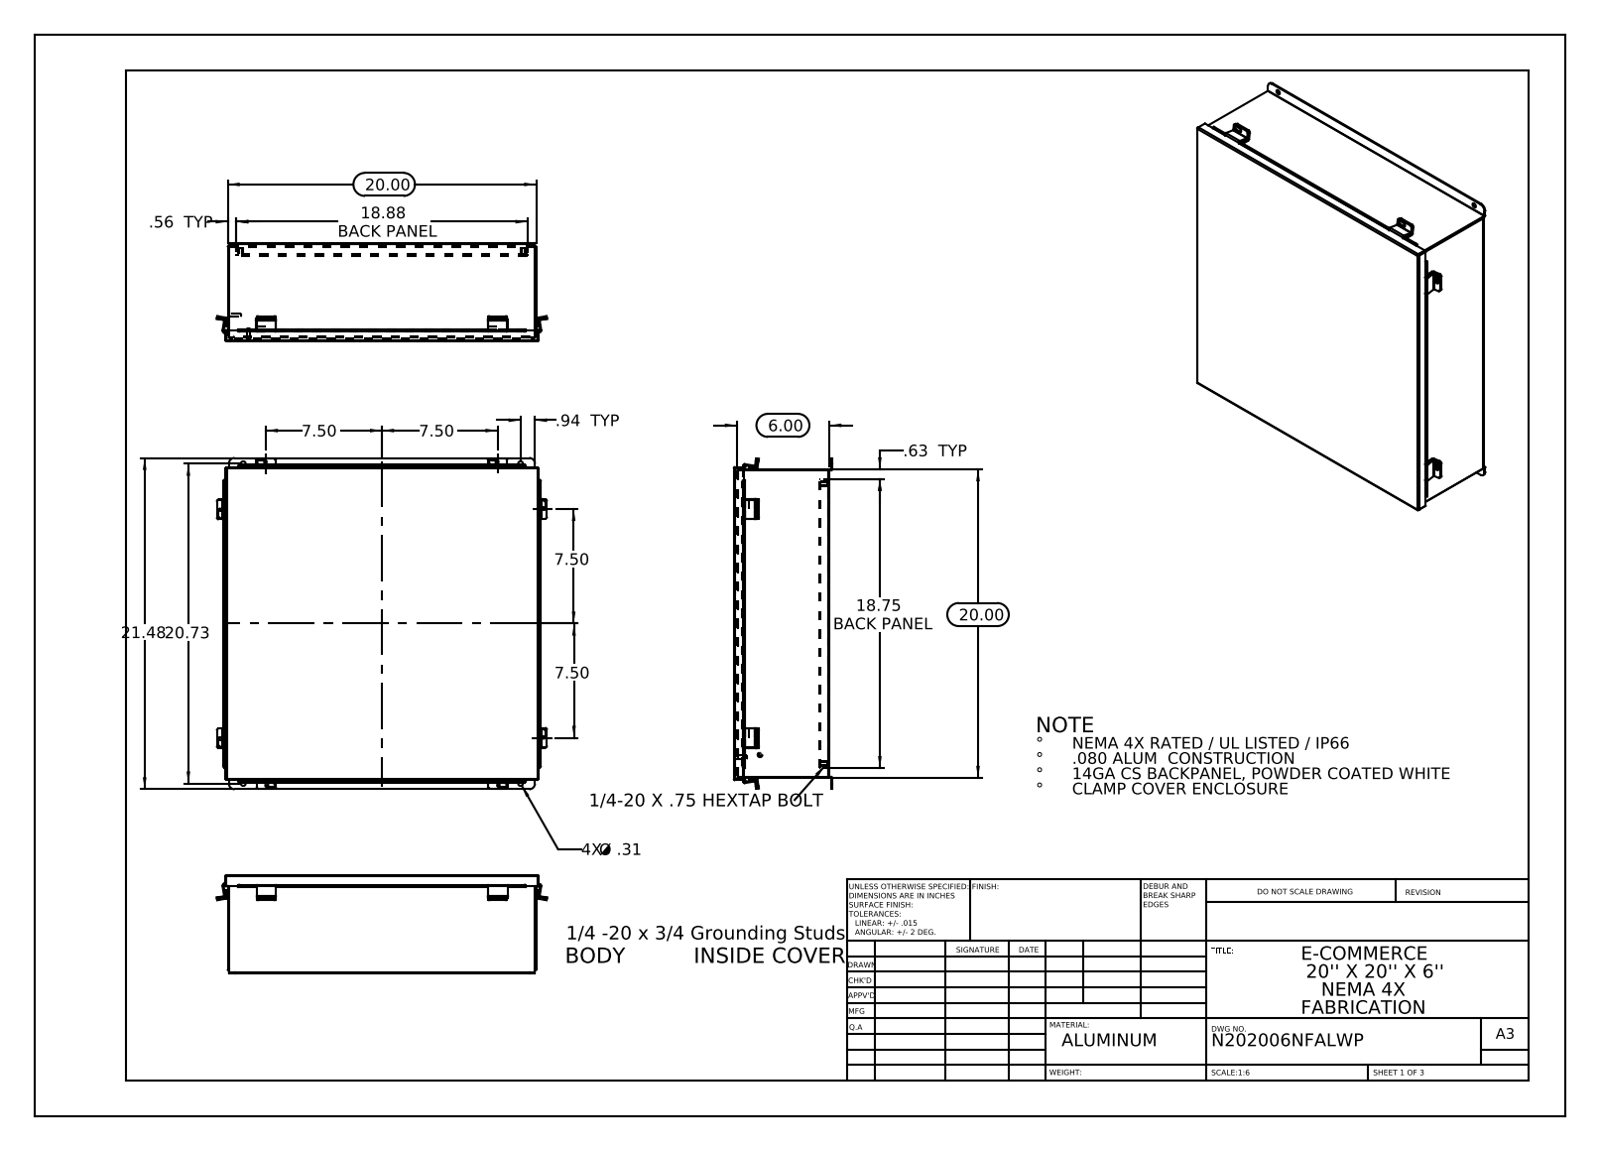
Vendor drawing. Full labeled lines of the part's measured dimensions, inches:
Part name (STEP PRODUCT): N202006NFSSWP; N202006NFSSWP JIC Bottom; N202006NFSSWP JIC Top; N202006NFSSWP JIC Cover Clamp (+6 more)
STEP written by: SolidWorks 2013 (CONFIG_CONTROL_DESIGN)
Units: inches
Bodies: 27 solids, 640 faces (420 planar, 200 cylindrical, 20 other)
Overall size (bounding box): 21.476 × 21.407 × 6.39
Volume: 133.3 in³ · Surface area: 3 597 in²
Round holes (diameter × count): ⌀0.25 ×12, ⌀0.187 ×4, ⌀0.312 ×4
Round bosses / shafts (diameter × count): ⌀0.313 ×4, ⌀0.315 ×2, ⌀0.236 ×2
Partial cylindrical surfaces — rounded edges, fillets, slot ends (radius × count): R0.125 ×28, R0.009 ×16, R0.133 ×16, R0.013 ×12, R0.088 ×12, R0.083 ×8, R0.1 ×8, R0.084 ×4
Main face-to-face distances: 0.075, 6.128, 19.925, 6.053, 6.203, 0.074, 5.628, 0.575, 0.5, 5.553
Hole centre spacings: 1.315, 18.222, 19.427, 26.603, 14.85, 15, 17.976, 18.126
